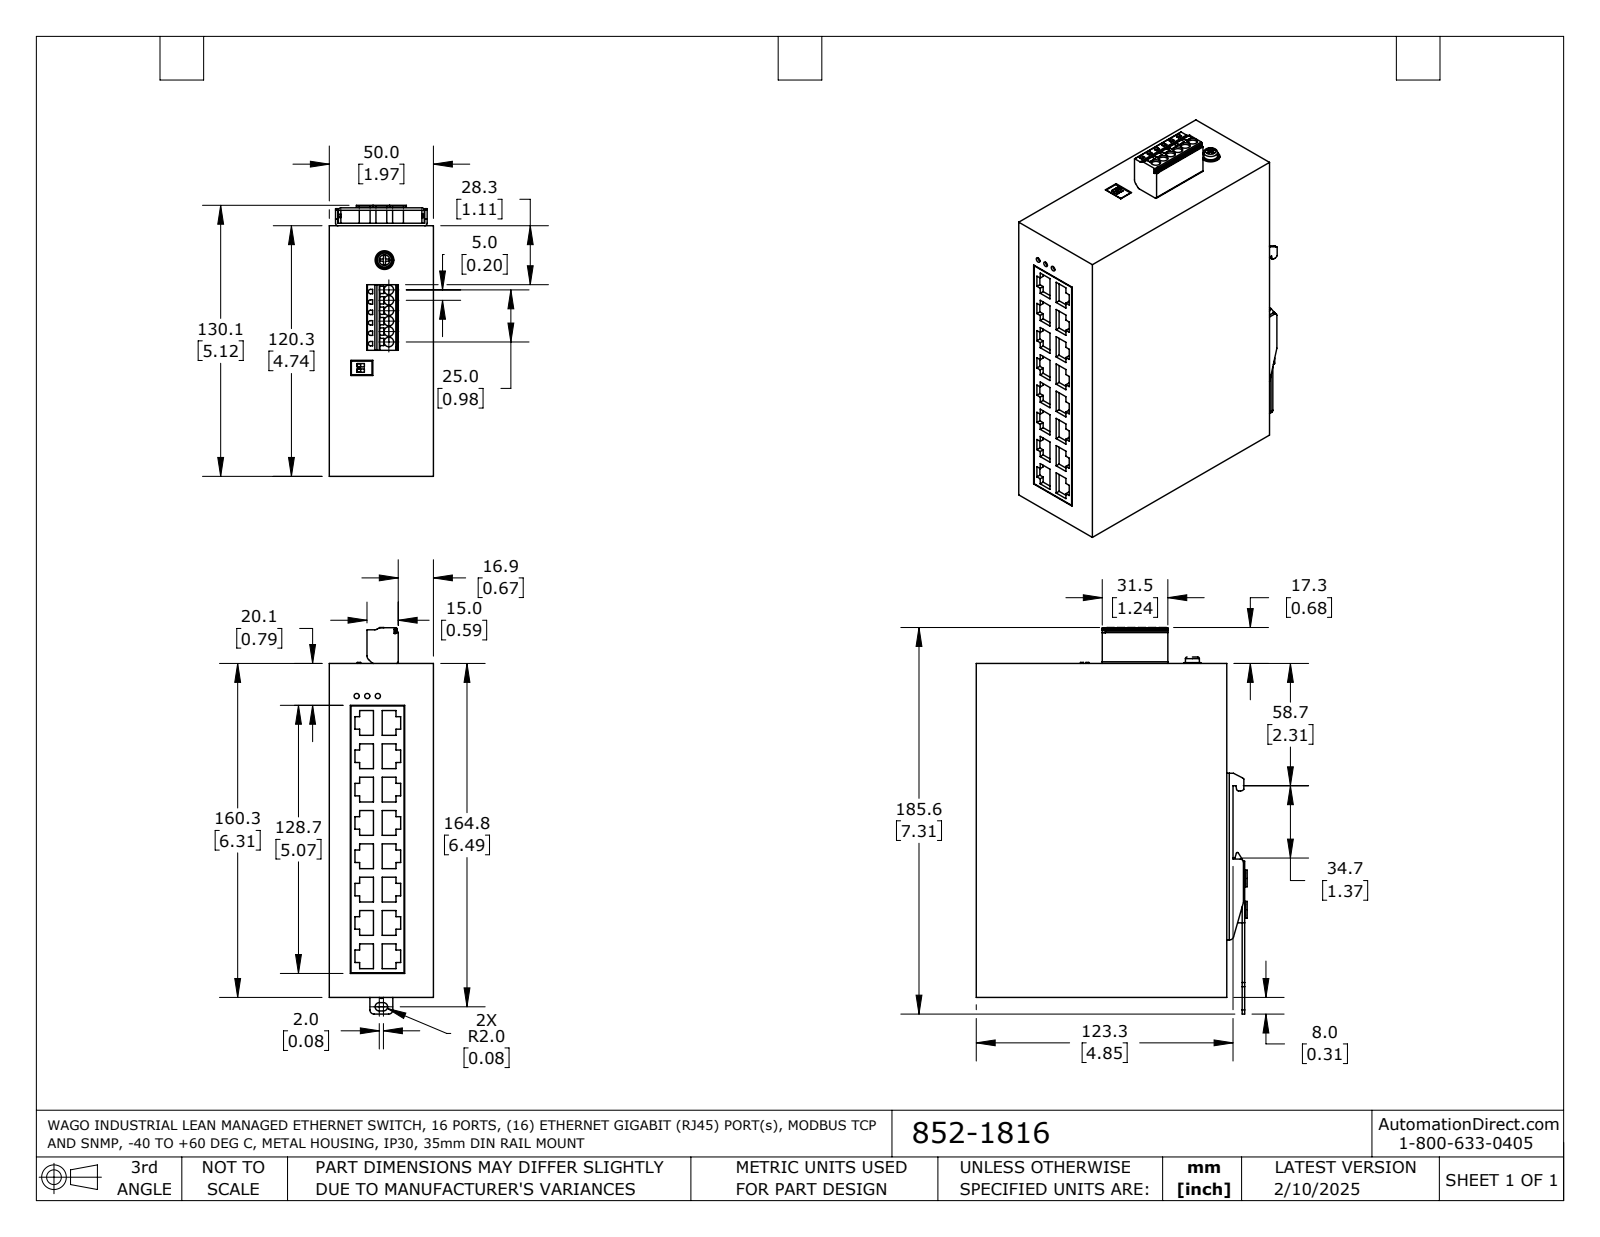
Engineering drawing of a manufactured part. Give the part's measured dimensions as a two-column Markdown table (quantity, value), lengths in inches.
| quantity | value |
| --- | --- |
| part name | 852-1816 |
| STEP written by | SolidWorks 2021 (AUTOMOTIVE_DESIGN) |
| units | inches |
| bodies | 1 solid, 466 faces (354 planar, 107 cylindrical, 5 other) |
| overall size | 7.305 × 5.122 × 1.969 |
| volume | 59.64 in³ |
| surface area | 123.4 in² |
| round holes (diameter × count) | 0.181 × 6, 0.098 × 3, 0.394 × 2, 0.102 × 1, 0.354 × 1 |
| round bosses / shafts (diameter × count) | 0.315 × 4, 0.205 × 3, 0.264 × 1 |
| partial cylindrical surfaces (radius × count) | 0.004 × 14, 0.079 × 10, 0.041 × 6, 0.104 × 6, 0.047 × 5, 0.02 × 4, 0.008 × 3, 0.031 × 1 |
| main face-to-face distances | 1.969, 0.047, 6.311, 4.736, 0.291, 4.783, 0.244, 0.339, 5.028, 5.075 |
| hole center spacings | 0.197, 0.394, 0.591, 0.2, 0.787, 1.297, 0.4, 0.569 |
